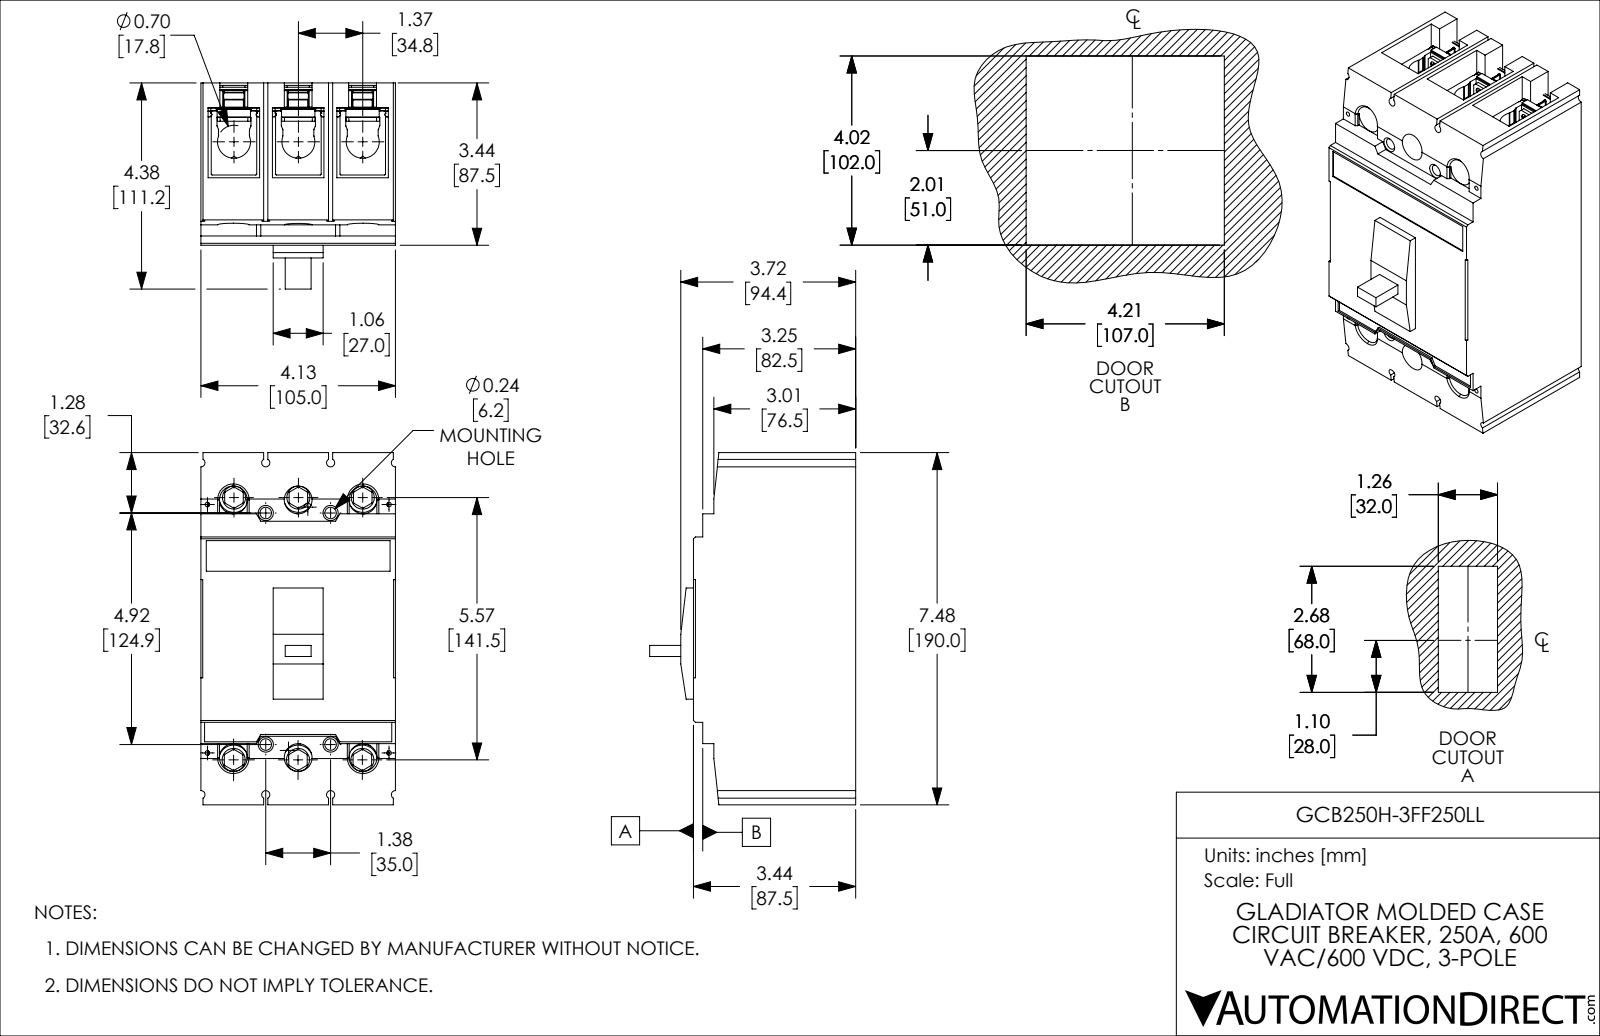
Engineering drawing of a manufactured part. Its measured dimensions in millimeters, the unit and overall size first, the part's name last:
Units: millimetres
Overall size (bounding box): 190 × 111.2 × 105
Round holes (diameter × count): ⌀1.7 ×24, ⌀4 ×24, ⌀2.5 ×10, ⌀9 ×6, ⌀15 ×6, ⌀17.5 ×6, ⌀4.4 ×4, ⌀6.2 ×4
Round bosses / shafts (diameter × count): ⌀18 ×6
Partial cylindrical surfaces — rounded edges, fillets, slot ends (radius × count): R0.3 ×206, R1 ×72, R1.5 ×36, R0.5 ×26, R0.2 ×24, R2 ×20, R0.4 ×12, R0.8 ×12
Main face-to-face distances: 34.7, 105, 69.5, 27.8, 21.4, 6.4, 1.5, 35, 155, 87.5
Hole centre spacings: 7.2, 18.9, 26.6, 35, 133.1, 160, 34.7, 36.2
Volume: 1 427 000 mm³ · Surface area: 203 700 mm²
Bodies: 25 solids, 2233 faces (975 planar, 958 cylindrical, 300 other)
Part name (STEP PRODUCT): GCB250H-3FF250LL
STEP written by: SolidWorks 2021 (CONFIG_CONTROL_DESIGN)
